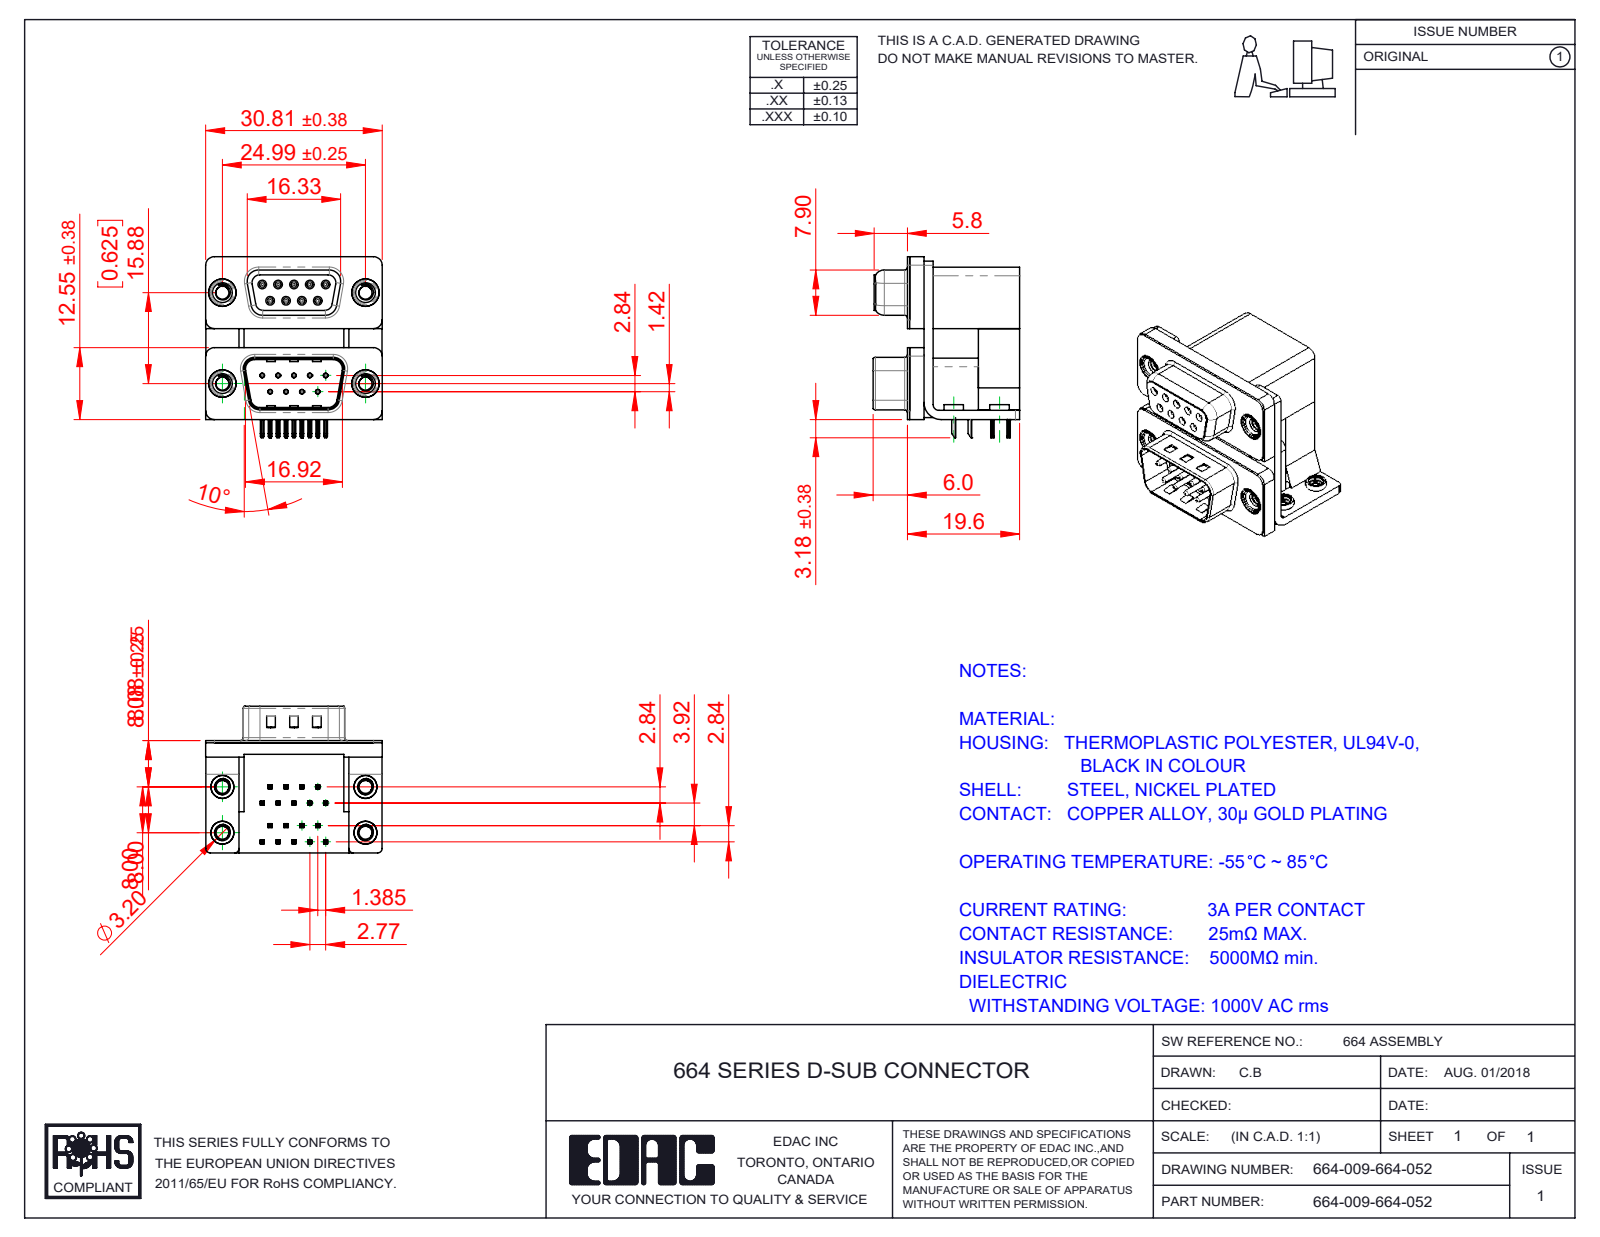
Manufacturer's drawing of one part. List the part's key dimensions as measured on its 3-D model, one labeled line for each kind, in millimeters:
Part name (STEP PRODUCT): 664 Contact Top Upper_L; 664 Housing Lower_09 Contacts; 664 Contact Bottom Lower; 664 4-40 Threaded Board Mount (+8 more)
STEP written by: SolidWorks 2020 (CONFIG_CONTROL_DESIGN)
Units: millimetres
Bodies: 33 solids, 2669 faces (1275 planar, 771 cylindrical, 623 other)
Overall size (bounding box): 31.61 × 30.81 × 25.6
Volume: 10 359 mm³ · Surface area: 12 382 mm²
Round holes (diameter × count): ⌀0.8 ×18, ⌀0.35 ×9, ⌀0.9 ×9, ⌀2.26 ×8, ⌀2.75 ×4, ⌀3.2 ×4, ⌀3.5 ×4, ⌀4 ×4, ⌀4.8 ×4, ⌀5 ×4
Round bosses / shafts (diameter × count): ⌀1.2 ×9, ⌀0.75 ×9, ⌀4.9 ×4, ⌀4.75 ×4, ⌀4 ×4, ⌀3.9 ×4, ⌀3.4 ×4
Partial cylindrical surfaces — rounded edges, fillets, slot ends (radius × count): R0.1 ×72, R0.15 ×36, R0.25 ×36, R0.12 ×18, R0.35 ×18, R1.5 ×13, R0.5 ×12, R1.35 ×10
Main face-to-face distances: 0.4, 2.5, 16.7, 19.2, 19.6, 2.9, 7.2, 9.5, 12, 12.4
Hole centre spacings: 3.16, 2.77, 16.12, 15.88, 5.54, 16.82, 13.11, 18.77
